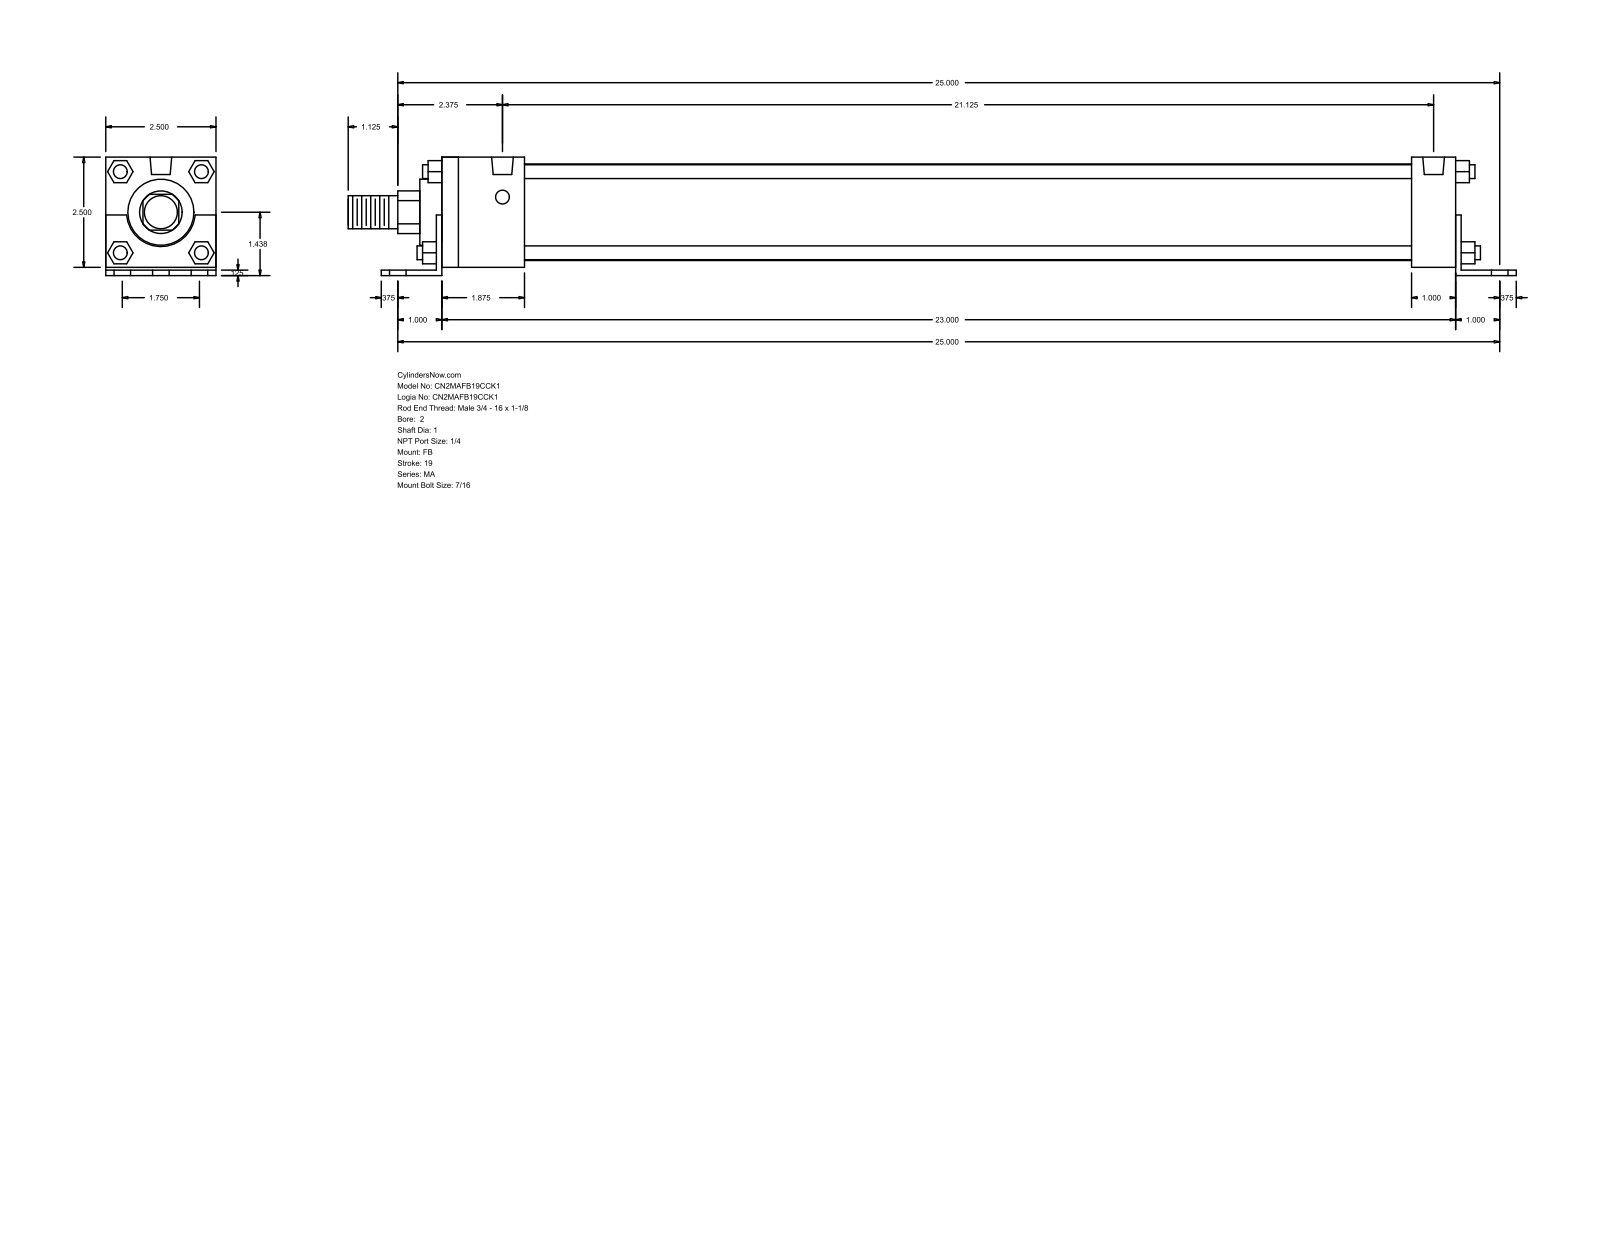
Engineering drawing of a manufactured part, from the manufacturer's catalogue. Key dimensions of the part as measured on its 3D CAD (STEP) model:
Part name (STEP PRODUCT): MA_FB__0200_1
STEP written by: GSSL Pune (CONFIG_CONTROL_DESIGN)
Units: millimetres
Bodies: 0 solids, 140 faces (105 planar, 35 cylindrical, 0 other)
Overall size (bounding box): 673.1 × 68.26 × 63.5
Round holes (diameter × count): ⌀11.11 ×6, ⌀7.94 ×4, ⌀12.49 ×2
Round bosses / shafts (diameter × count): ⌀7.94 ×4, ⌀55.63 ×1, ⌀38.1 ×1, ⌀25.4 ×1, ⌀19.05 ×1
Partial cylindrical surfaces — rounded edges, fillets, slot ends (radius × count): R12.29 ×1, R19.81 ×1
Main face-to-face distances: 63.5, 3.17, 4.76, 68.26, 1.59, 65.09, 587.37, 12.7, 584.2, 28.57
Hole centre spacings: 22.23, 635.39, 635, 44.11, 44.46, 64.3, 536.57, 575.1
